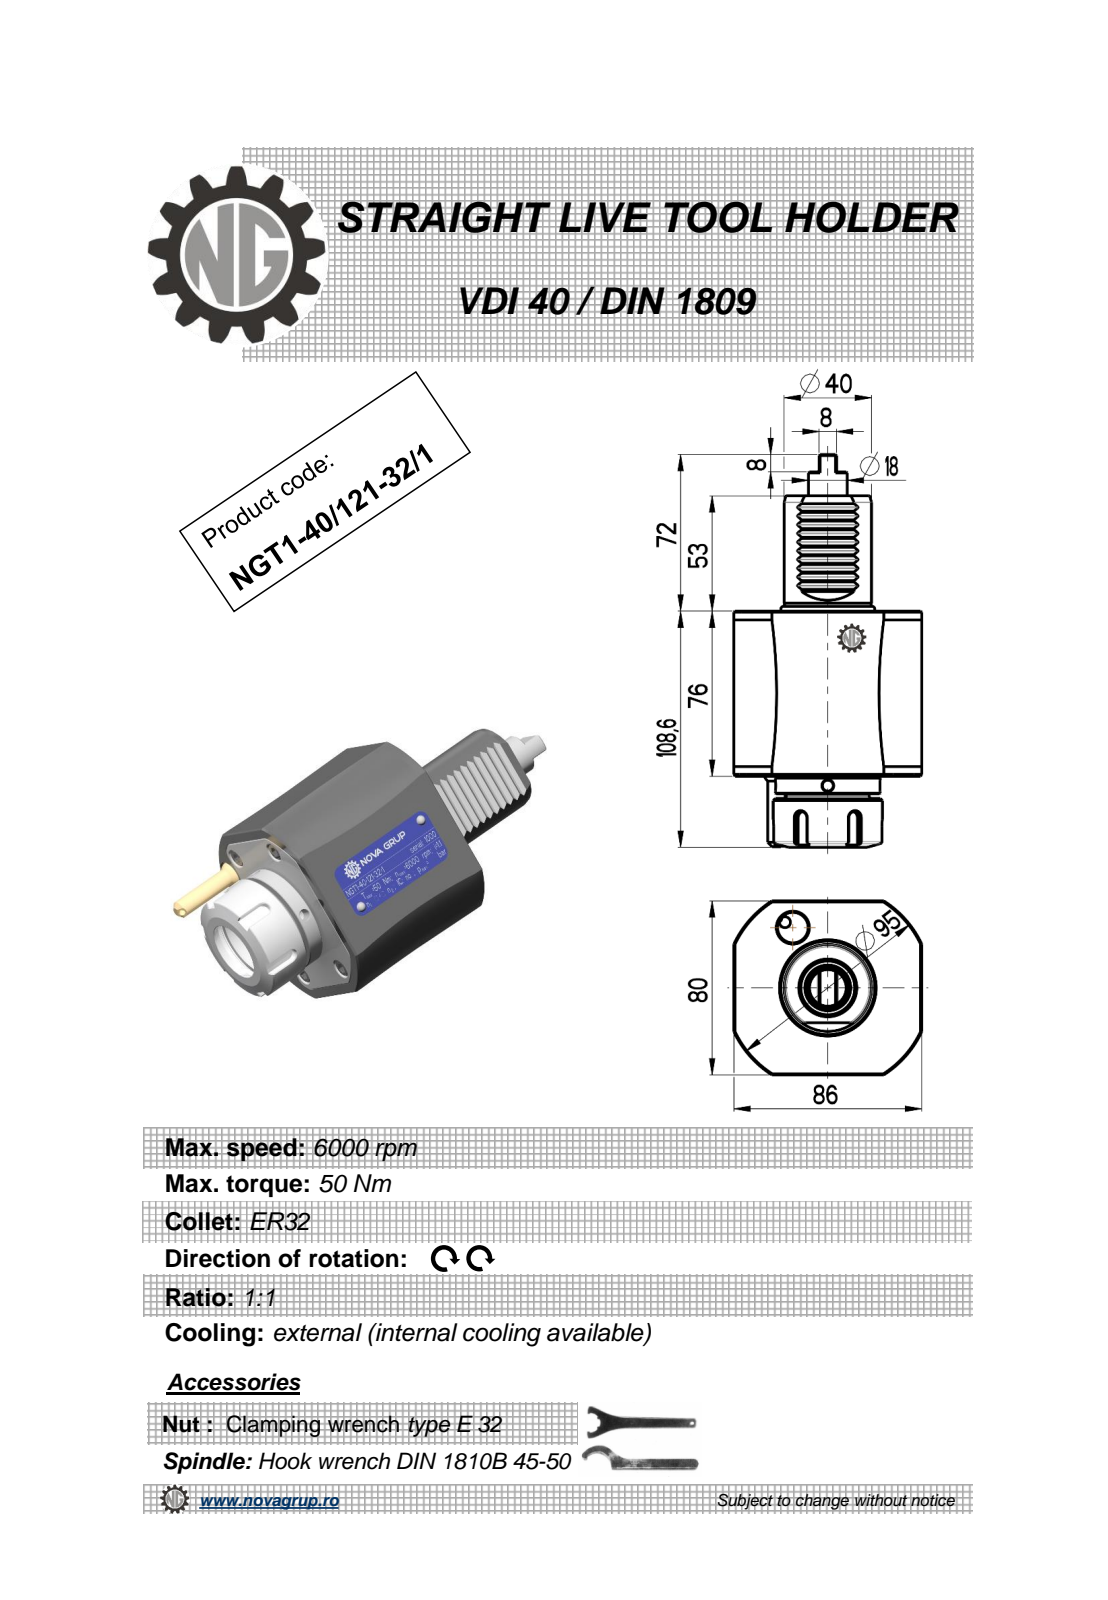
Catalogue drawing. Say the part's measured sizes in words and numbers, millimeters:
The part is named "NGT1_40_121_32_1". Its 3-D file was written by "PRO/ENGINEER BY PARAMETRIC TECHNOLOGY CORPORATION, 2010280 (CONFIG_CONTROL_DESIGN)". It is 1 solid with 251 faces: 102 planar, 64 cylindrical and 85 other. Overall it measures 180.6 by 86 by 81.6 millimeters. Its volume is 598 185 cubic millimeters and its surface area 51 851 square millimeters. Round holes: 3 of diameter 5, 1 of diameter 3, 1 of diameter 27. Round bosses or shafts: 1 of diameter 50, 1 of diameter 48, 1 of diameter 41.5, 1 of diameter 41, 1 of diameter 40, 1 of diameter 17.8, 1 of diameter 8. Partial cylindrical surfaces (rounded edges, fillets, slot ends): 10 of radius 0.3, 6 of radius 0.22, 5 of radius 3, 2 of radius 0.8, 1 of radius 47.5. The main face-to-face distances are 76, 80, 86, 2.83, 53, 129, 157.1, 104.1, 28.1, 5.66. The hole center spacings are 40.
